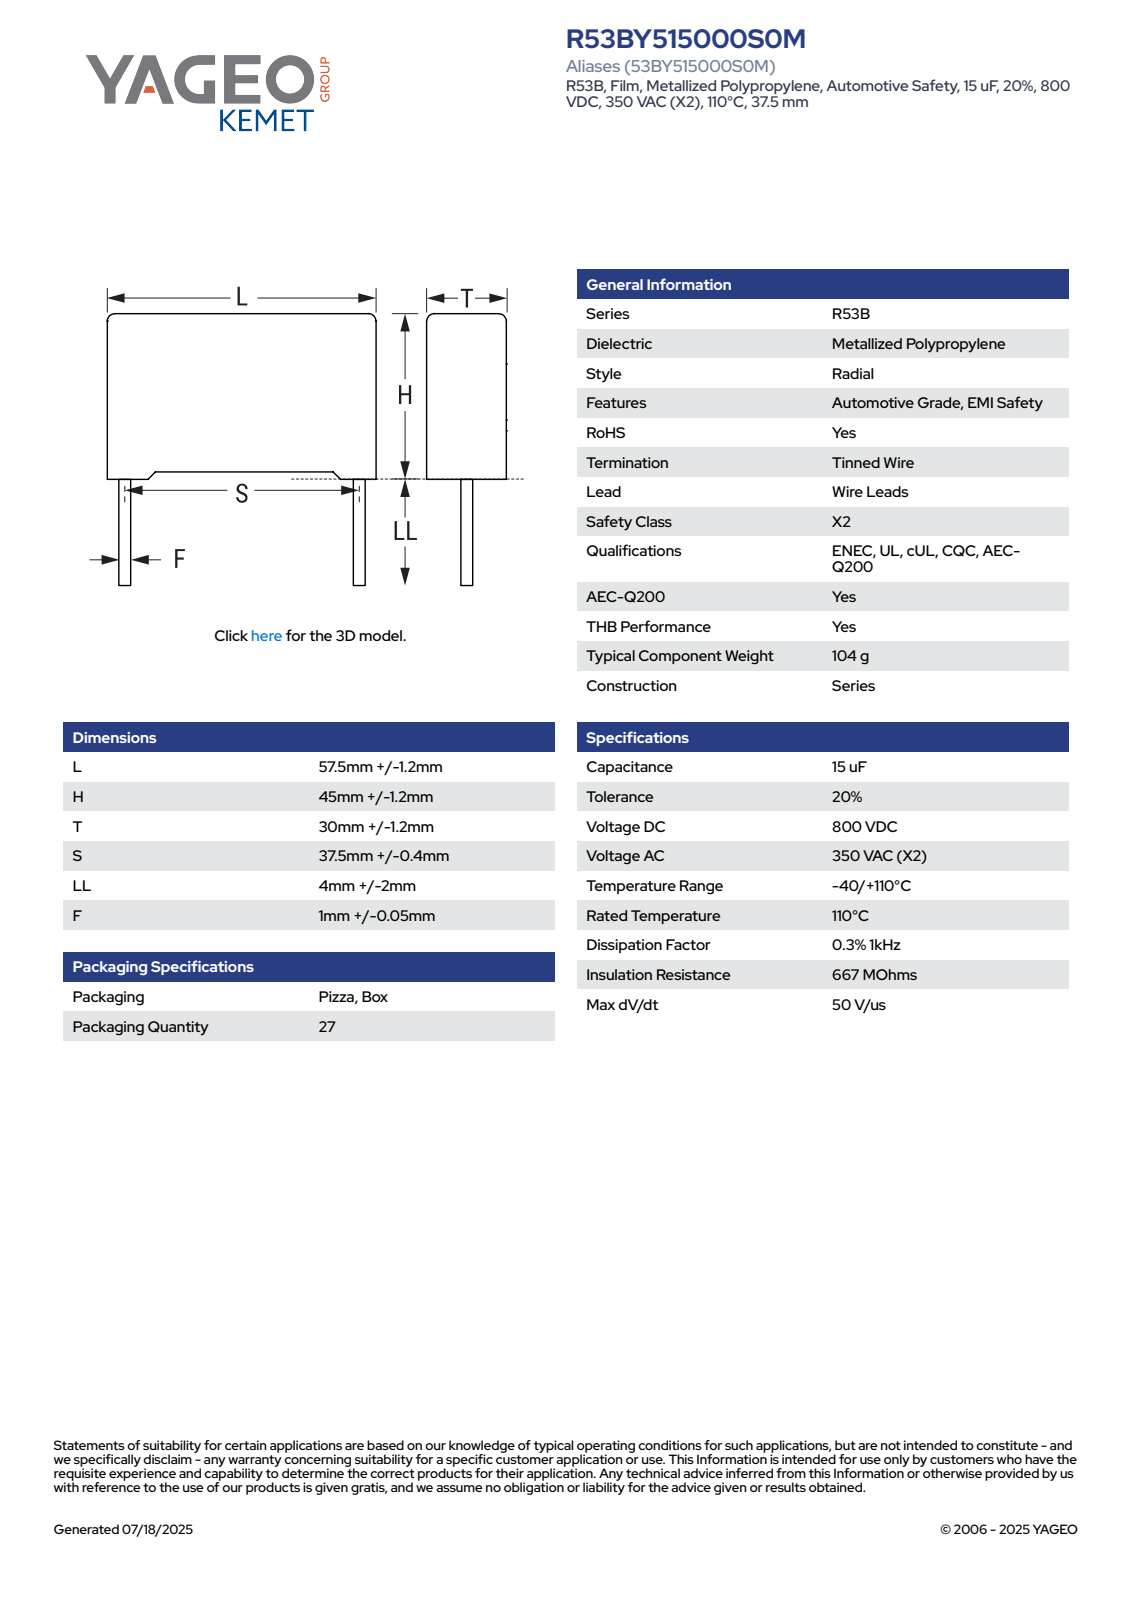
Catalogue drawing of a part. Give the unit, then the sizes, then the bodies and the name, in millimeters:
Units: millimetres
Overall size (bounding box): 58.7 × 52.2 × 31.2
Round bosses / shafts (diameter × count): ⌀1.05 ×2
Partial cylindrical surfaces — rounded edges, fillets, slot ends (radius × count): R0.5 ×4
Main face-to-face distances: 31.2, 58.7, 44.61, 0.84, 45.45, 0.75, 1.59, 46.2, 1.96, 31.21
Volume: 82 551 mm³ · Surface area: 12 224 mm²
Bodies: 4 solids, 85 faces (77 planar, 8 cylindrical, 0 other)
Part name (STEP PRODUCT): CFR_RB2_57.5X45X30_L58.7H46.2T31.2S37.5LL6F1.05
STEP written by: SolidWorks 2021 (AUTOMOTIVE_DESIGN)
